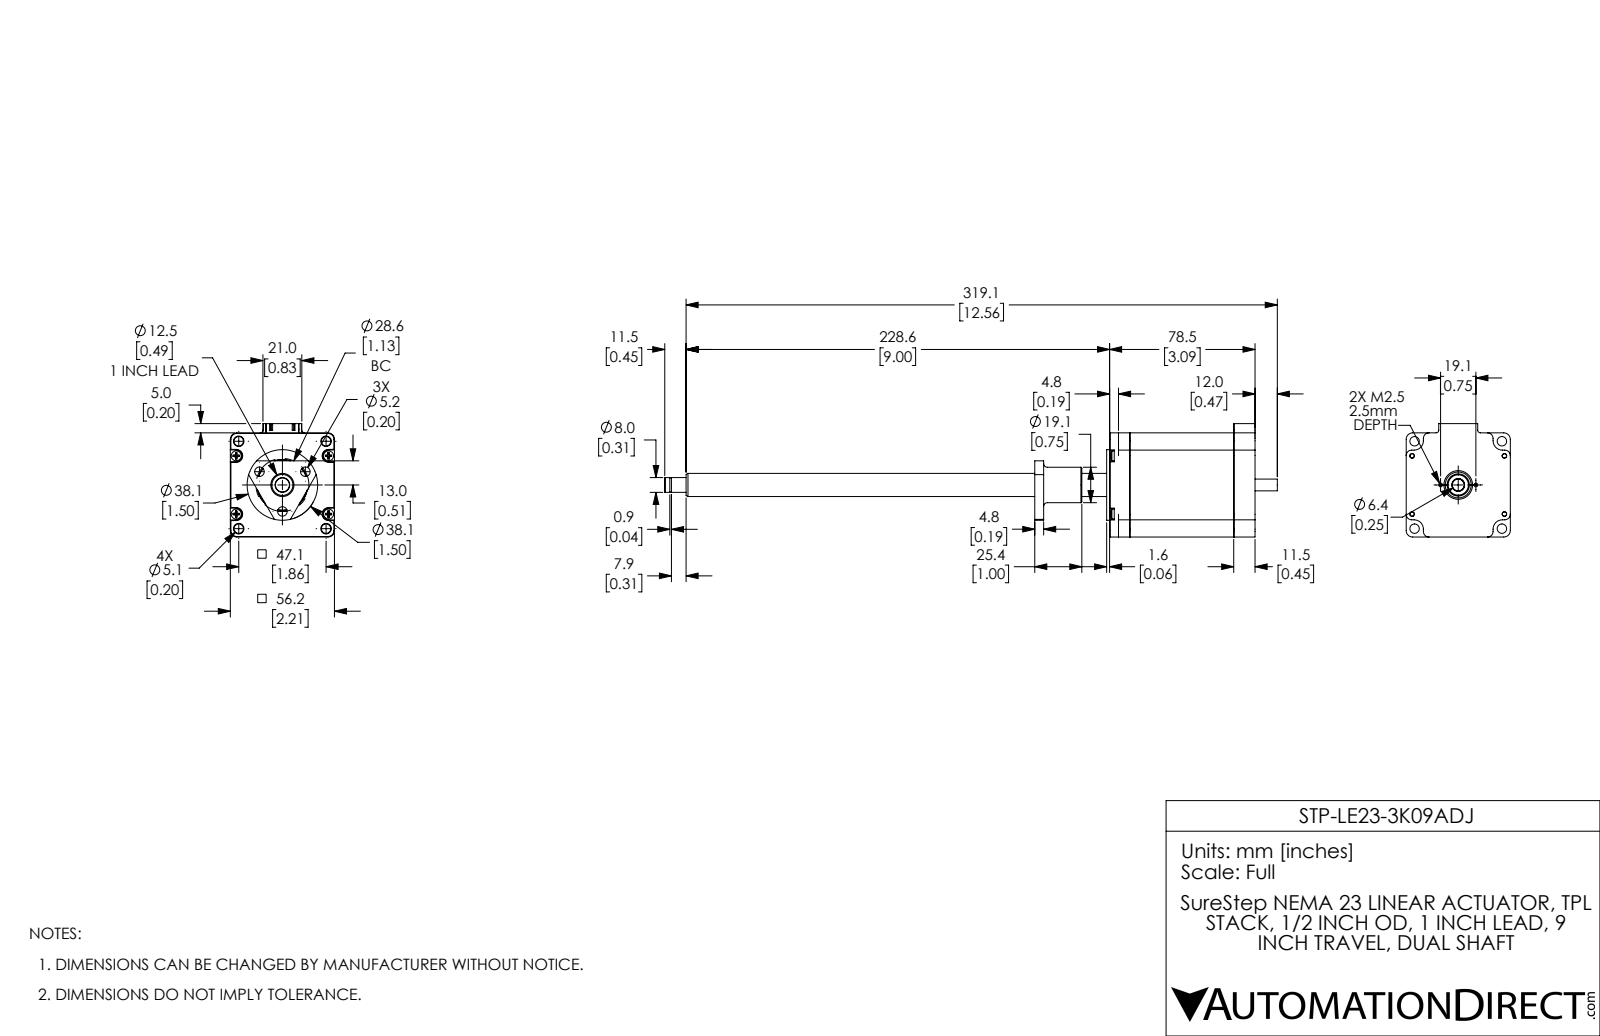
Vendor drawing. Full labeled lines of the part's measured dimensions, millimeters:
Part name (STEP PRODUCT): STP-LE23-3K09ADJ; STP-LE23-3K09ADJ_2; STP-LE23-3K09ADJ_1
STEP written by: SolidWorks 2017 (AUTOMOTIVE_DESIGN)
Units: millimetres
Bodies: 7 solids, 1001 faces (380 planar, 460 cylindrical, 161 other)
Overall size (bounding box): 330.6 × 61.2 × 56.2
Volume: 236 678 mm³ · Surface area: 66 334 mm²
Round holes (diameter × count): ⌀4.5 ×8, ⌀2.5 ×4, ⌀3.3 ×4, ⌀5.1 ×4, ⌀5.16 ×3, ⌀2 ×2, ⌀2.05 ×2, ⌀6.9 ×1, ⌀10.5 ×1, ⌀14.8 ×1, ⌀15.5 ×1, ⌀16 ×1
Round bosses / shafts (diameter × count): ⌀5.4 ×4, ⌀2.91 ×4, ⌀38.1 ×1, ⌀36 ×1, ⌀35.6 ×1, ⌀34.85 ×1, ⌀28 ×1, ⌀19.1 ×1
Partial cylindrical surfaces — rounded edges, fillets, slot ends (radius × count): R1.5 ×10, R0.2 ×8, R3 ×8, R1.8 ×4, R3.2 ×4, R3.5 ×4, R5 ×4, R0.6 ×1
Main face-to-face distances: 56.2, 56, 11.5, 67.5, 78.5, 11, 51.4, 67, 1.6, 1.1
Hole centre spacings: 24.75, 14.12, 33.05, 35.01, 45.74, 48.53, 56.99, 6.55
